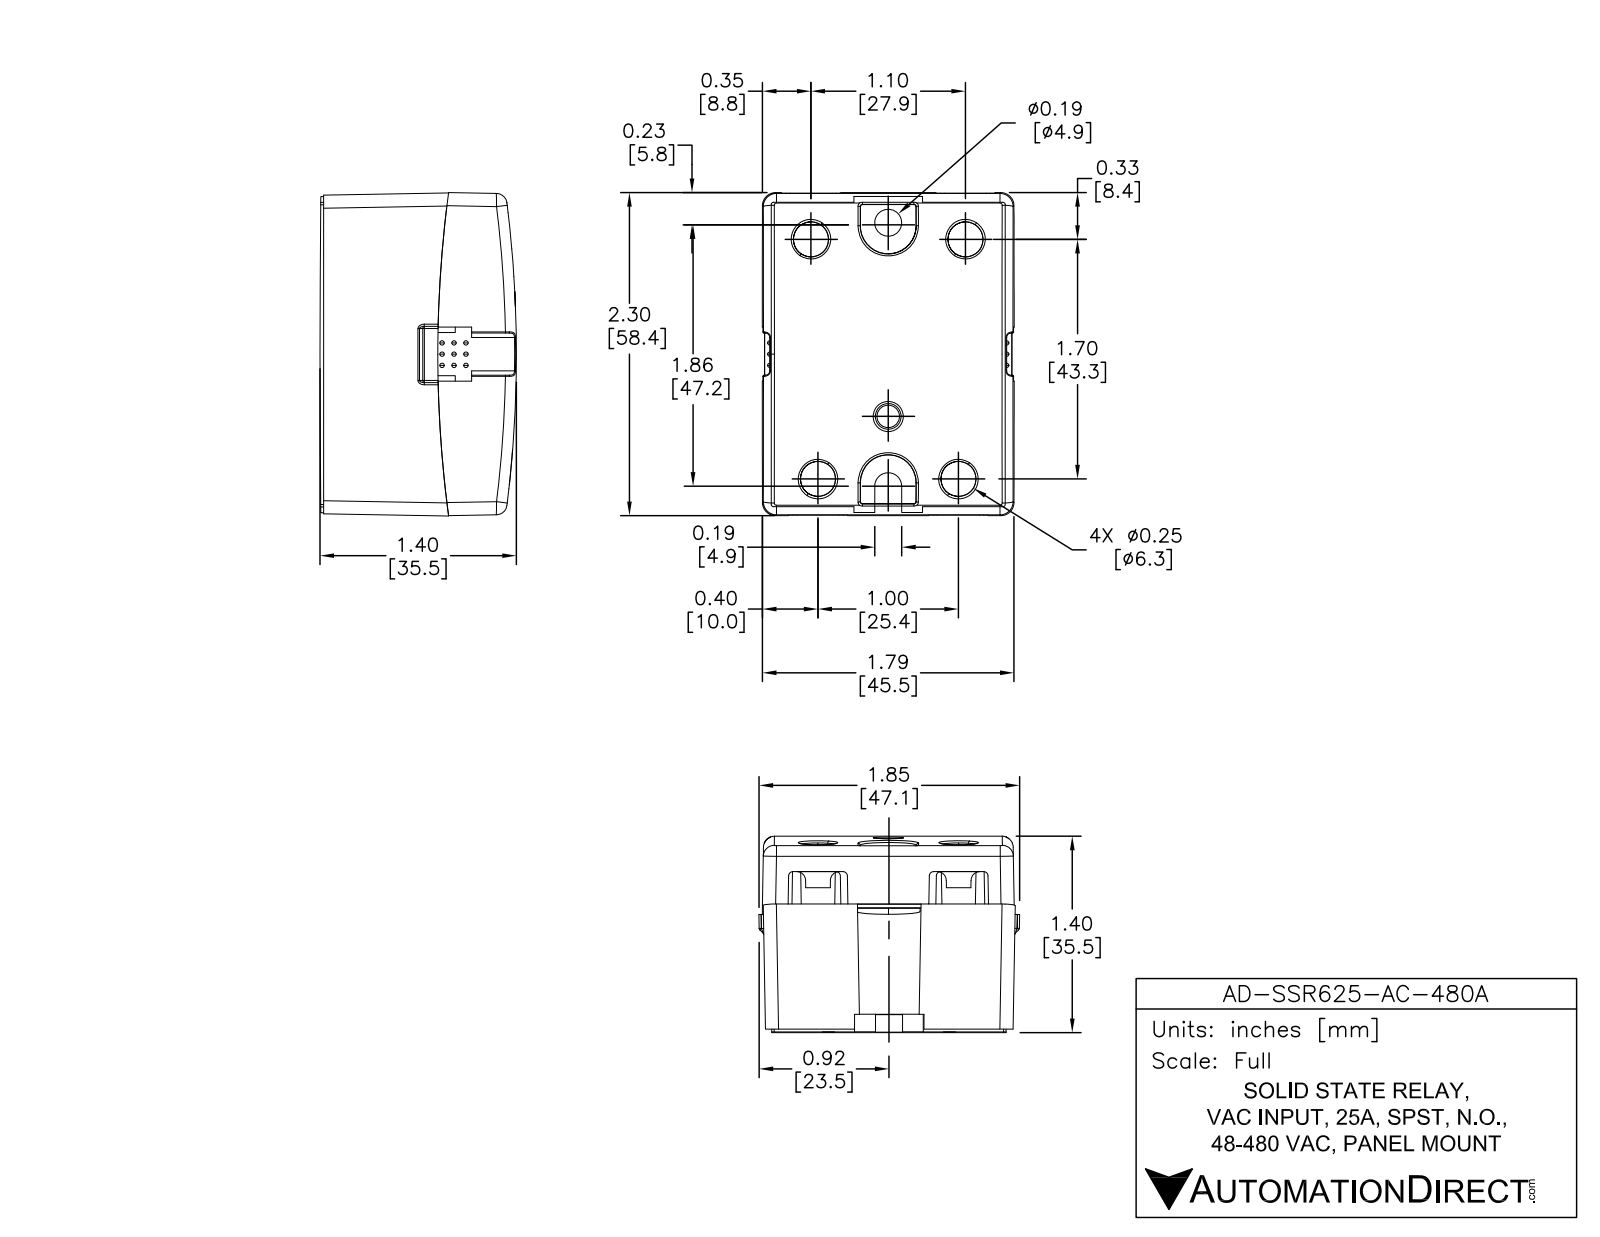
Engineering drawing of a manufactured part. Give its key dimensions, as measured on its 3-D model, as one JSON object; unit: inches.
{"part_name": "AD-SSR625-AC-480A", "step_written_by": "SolidWorks 2013 (AUTOMOTIVE_DESIGN)", "units": "inches", "bodies": {"solids": 3, "faces": 251, "planar": 145, "cylindrical": 95, "other": 11}, "overall_size": [2.3, 1.79, 1.4], "volume_in3": 5.14, "surface_area_in2": 26.41, "round_holes": [[0.25, 4], [0.19, 1]], "round_bosses_or_shafts": [[0.4, 2], [0.35, 2], [0.3, 2], [0.25, 2], [0.2, 2], [0.2, 2]], "partial_cylinders_radius": [[0.03, 6], [0.01, 4], [0.04, 4], [0.5, 4], [0.194, 2], [0.095, 1], [0.5, 1], [0.5, 1]], "face_to_face_distances": [1.79, 2.3, 1.166, 0.25, 0.916, 0.671, 1.059, 0.5, 1.8, 0.08], "hole_center_spacings": [0.556, 0.565, 1, 1.1, 1.7, 1.701, 1.876, 1.879]}
